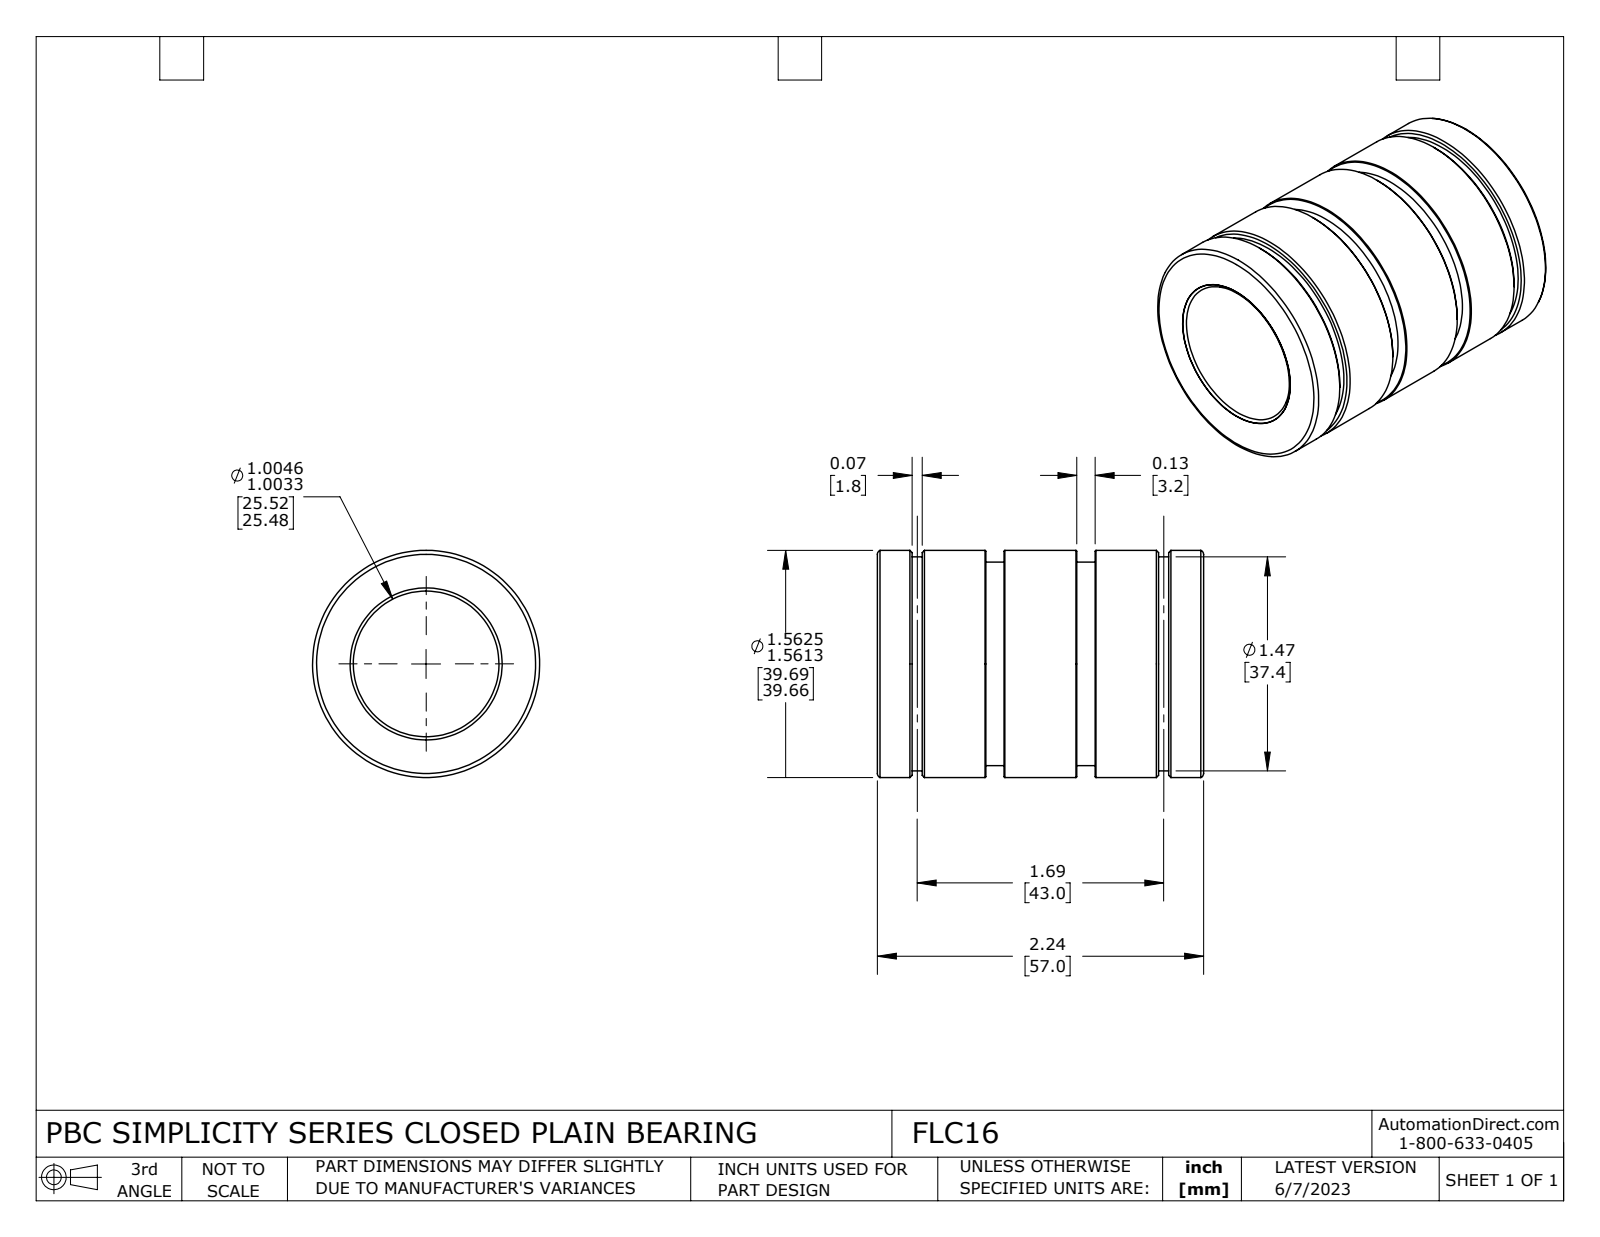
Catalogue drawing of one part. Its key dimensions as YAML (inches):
part_name: "FLC16"
step_written_by: "SolidWorks 2021 (CONFIG_CONTROL_DESIGN)"
units: inches
bodies: {solids: 2, faces: 58, planar: 10, cylindrical: 24, other: 24}
overall_size: [2.242, 1.562, 1.562]
volume: 2.399
surface_area: 36.83
round_holes:
  - {diameter: 1.001, count: 1}
  - {diameter: 1.045, count: 1}
round_bosses_or_shafts:
  - {diameter: 1.562, count: 1}
  - {diameter: 1.471, count: 1}
  - {diameter: 1.399, count: 1}
face_to_face_distances: [2.243, 0.871, 1.371, 0.745, 1.497, 0.126, 0.626, 0.5, 0.752, 0.309]
